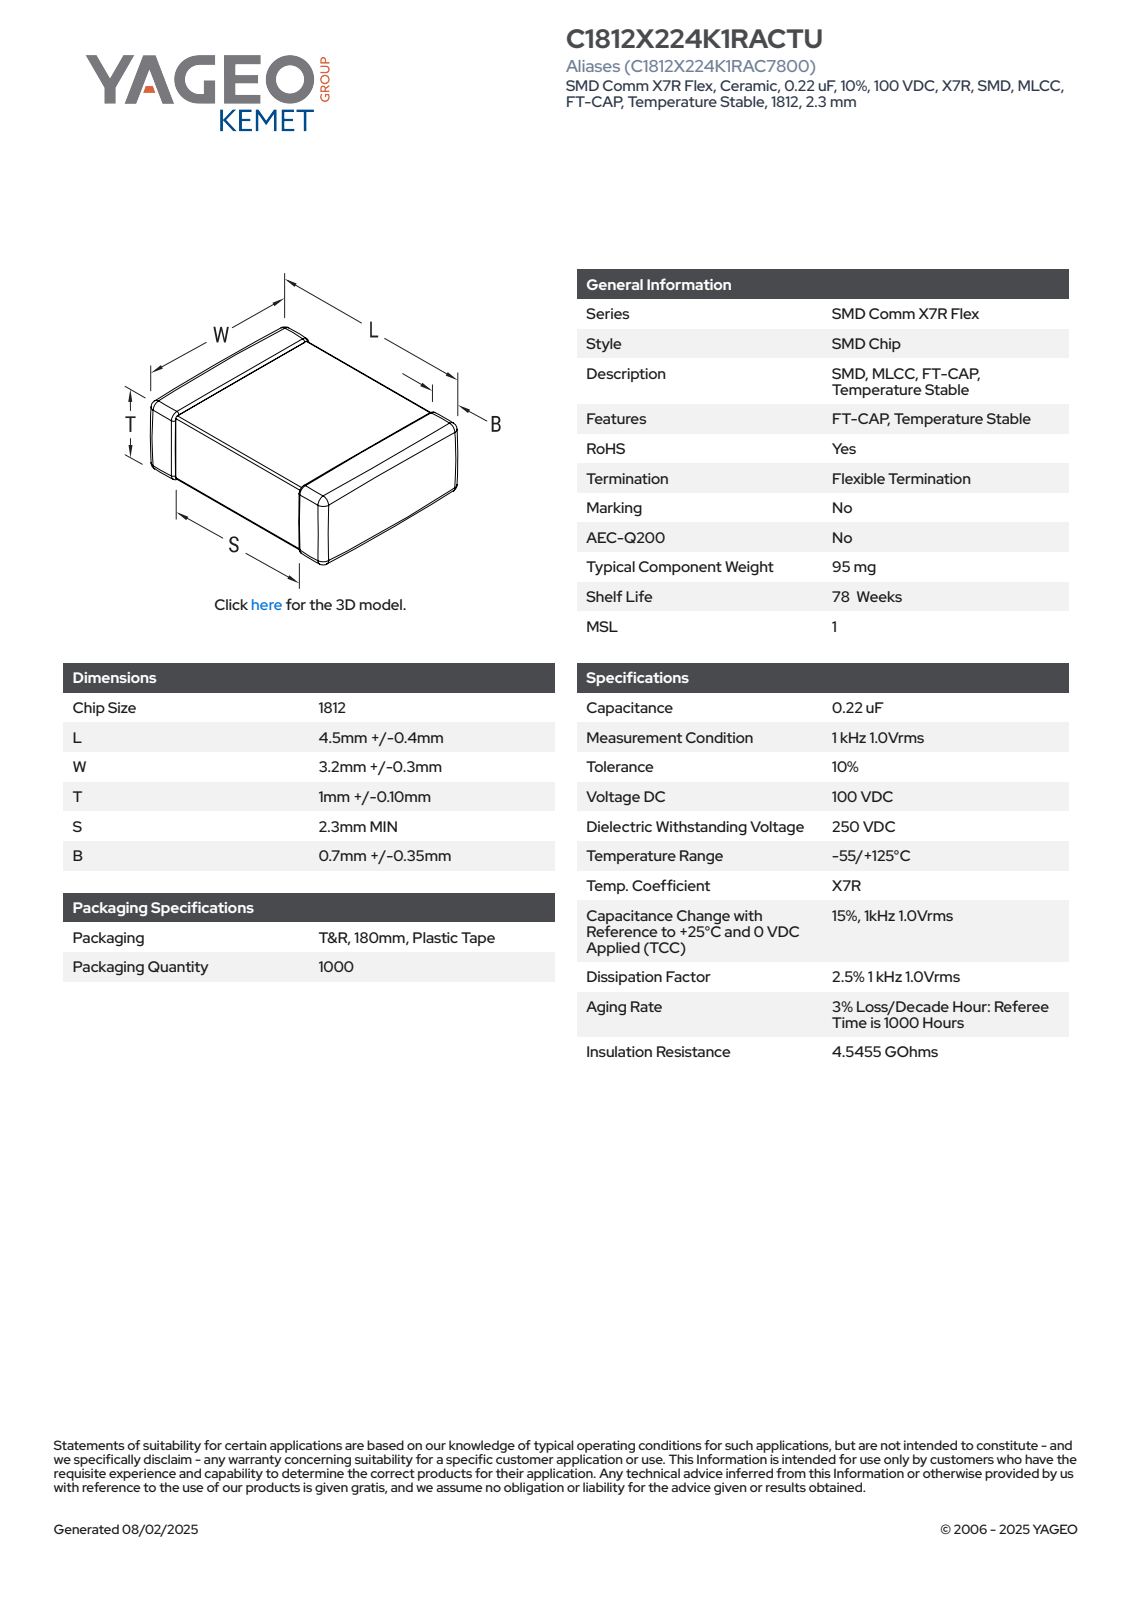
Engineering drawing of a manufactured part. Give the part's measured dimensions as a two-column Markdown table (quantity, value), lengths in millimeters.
| quantity | value |
| --- | --- |
| part name | CCS_CCSTDNOS_1812_L4.9W3.5T1.1B1.05 |
| STEP written by | SolidWorks 2014 (AUTOMOTIVE_DESIGN) |
| units | millimeters |
| bodies | 4 solids, 125 faces (71 planar, 38 cylindrical, 16 other) |
| overall size | 4.9 × 3.5 × 1.1 |
| volume | 17 mm³ |
| surface area | 51 mm² |
| main face-to-face distances | 1.03, 0.96, 1.1, 3.43, 4.9, 3.36, 3.5, 1.42, 1.94, 1.49 |
